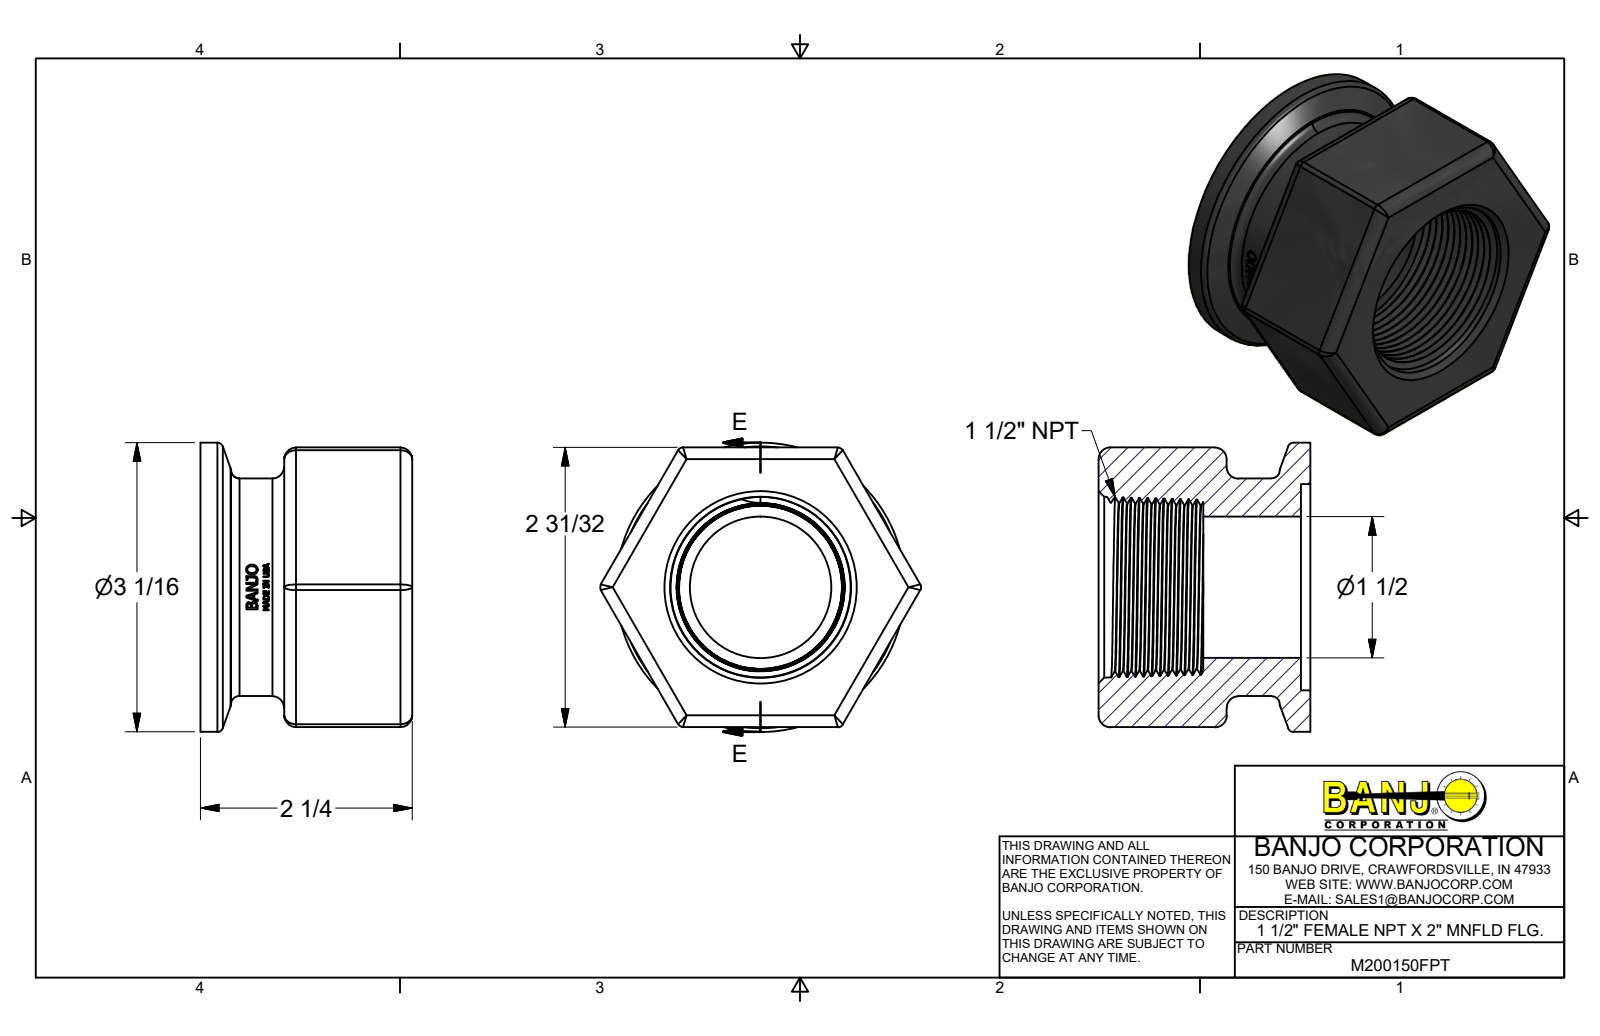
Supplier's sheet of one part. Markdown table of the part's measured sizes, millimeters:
| quantity | value |
| --- | --- |
| part name | M200150FPT |
| STEP written by | Autodesk Inventor 2017 (AUTOMOTIVE_DESIGN) |
| units | millimeters |
| bodies | 1 solid, 423 faces (196 planar, 58 cylindrical, 169 other) |
| overall size | 86.64 × 77.98 × 57.15 |
| volume | 161 036 mm³ |
| surface area | 34 288 mm² |
| round holes (diameter × count) | 38.1 × 1, 55.63 × 1 |
| round bosses / shafts (diameter × count) | 77.98 × 1, 58.67 × 1 |
| partial cylindrical surfaces (radius × count) | 3.17 × 12, 1.52 × 6, 13.81 × 1, 28.57 × 1 |
| main face-to-face distances | 75.44, 57.15, 54.61, 2.54, 34.54, 20.07, 22.61, 28.27, 6.27, 26.34 |
